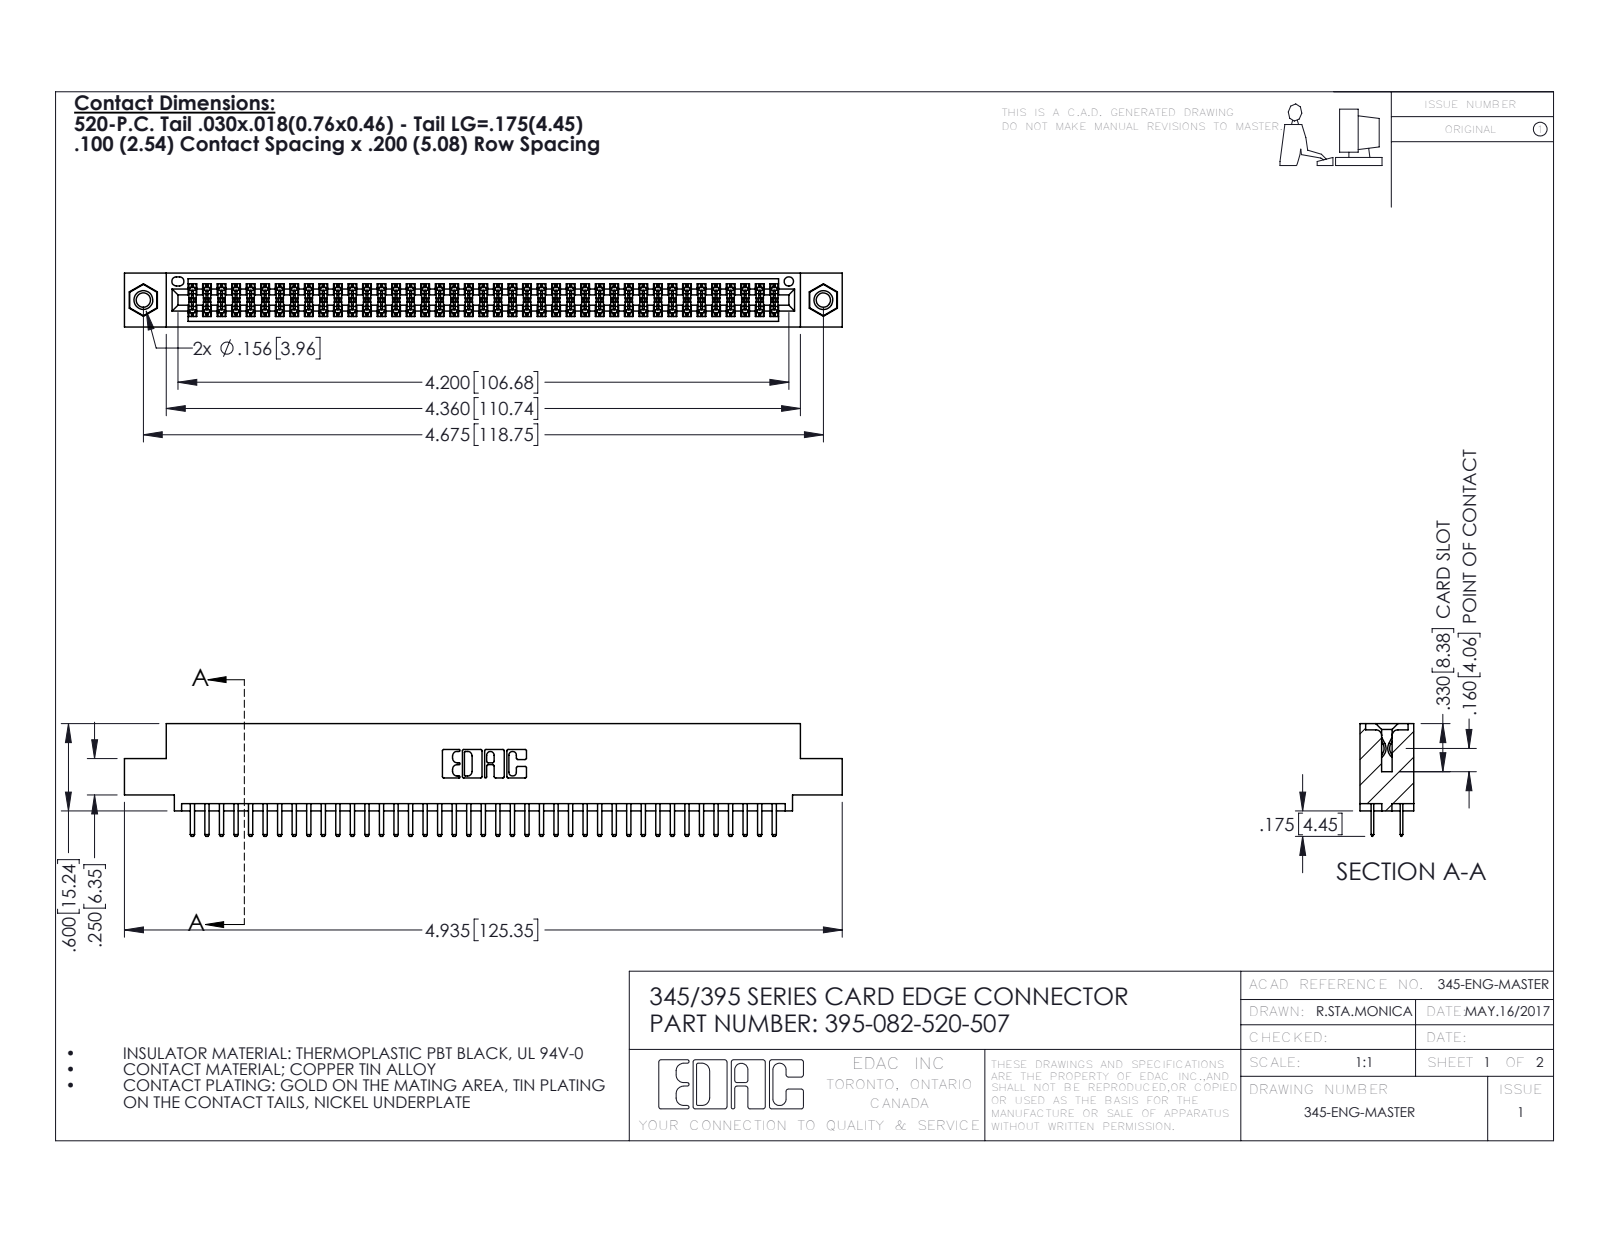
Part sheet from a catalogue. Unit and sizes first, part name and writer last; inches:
Units: inches
Overall size (bounding box): 4.935 × 0.775 × 0.37
Round holes (diameter × count): ⌀0.098 ×2, ⌀0.125 ×2, ⌀0.156 ×2, ⌀0.064 ×1
Round bosses / shafts (diameter × count): ⌀0.155 ×2
Partial cylindrical surfaces — rounded edges, fillets, slot ends (radius × count): R0.006 ×123, R0.01 ×86, R0.01 ×22, R0.007 ×6, R0.031 ×6, R0.026 ×3, R0.014 ×2, R0.019 ×2
Main face-to-face distances: 0.072, 0.298, 0.2, 0.37, 0.098, 0.272, 0.025, 0.225, 0.022, 0.072
Hole centre spacings: 0.27, 4.439, 4.675
Volume: 0.735 in³ · Surface area: 27.63 in²
Bodies: 85 solids, 4618 faces (2986 planar, 1616 cylindrical, 16 other)
Part name (STEP PRODUCT): 395-082-520-507; 345-250-001_345-250-005-103; 345 Part_0.110 Offset - 0.156 Dia-TI; 345-292-001_345-293-120
STEP written by: SolidWorks 2016 (CONFIG_CONTROL_DESIGN)
